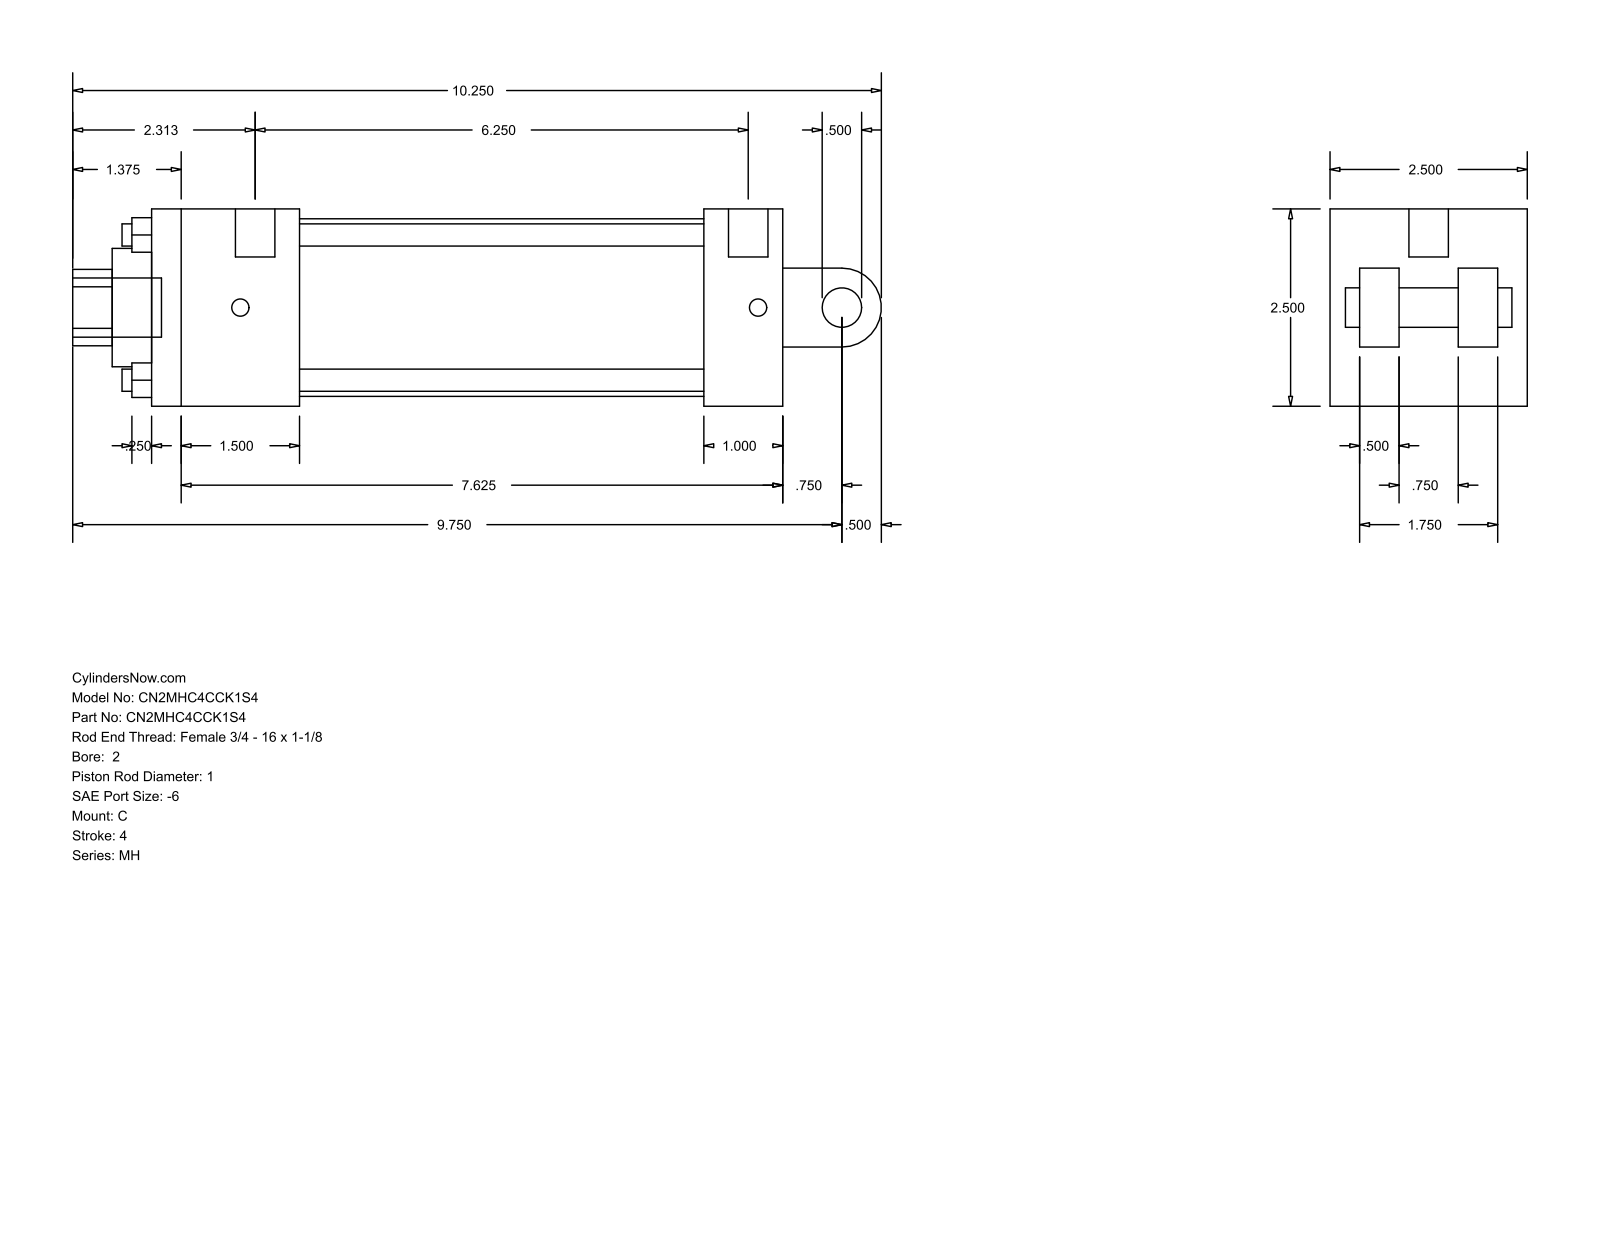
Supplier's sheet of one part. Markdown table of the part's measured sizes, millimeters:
| quantity | value |
| --- | --- |
| part name | MH_C__0200_1 |
| STEP written by | GSSL Pune (CONFIG_CONTROL_DESIGN) |
| units | millimeters |
| bodies | 0 solids, 99 faces (70 planar, 29 cylindrical, 0 other) |
| overall size | 260.35 × 63.5 × 63.5 |
| round holes (diameter × count) | 7.14 × 4, 5.56 × 2, 12.7 × 1, 25.4 × 1, 38.1 × 1, 57.15 × 1 |
| round bosses / shafts (diameter × count) | 12.7 × 2, 5.56 × 2, 19.05 × 1 |
| partial cylindrical surfaces (radius × count) | 12.29 × 1, 12.7 × 1 |
| main face-to-face distances | 63.5, 203.2, 12.7, 25.4, 9.52, 47.63, 53.98, 177.8, 130.17, 155.57 |
| hole center spacings | 33.05, 46.74, 66.1, 3.17 |
